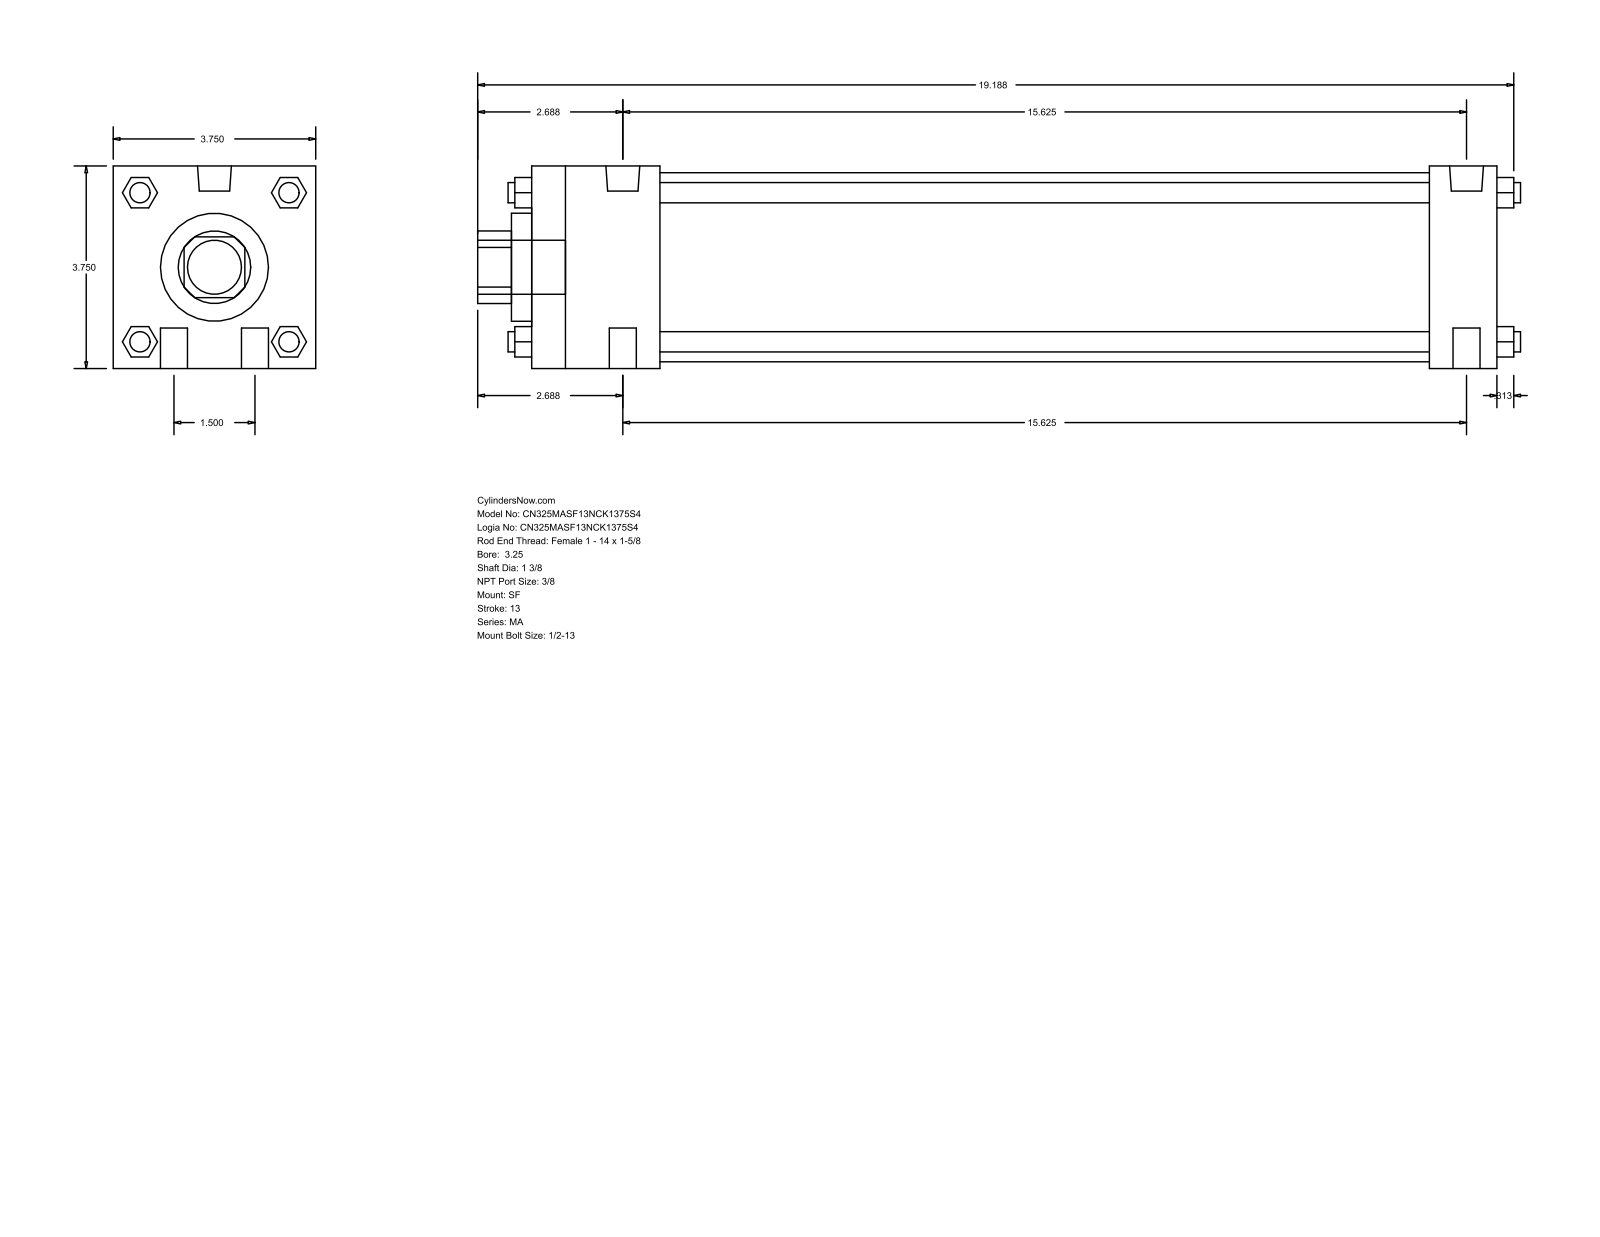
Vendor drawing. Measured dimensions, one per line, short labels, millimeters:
name: MA_SF__0325_1.375
written by: GSSL Pune (CONFIG_CONTROL_DESIGN)
unit: mm
bodies: 0 solids, 124 faces (94 planar, 30 cylindrical, 0 other)
size: 490.54 × 95.25 × 95.25
holes: 1× ⌀34.92, 1× ⌀50.8, 1× ⌀88.9
bosses: 4× ⌀12.7, 4× ⌀9.53, 2× ⌀15.93, 2× ⌀11.11, 1× ⌀25.4
rounds: 1× R17.06
face distances: 95.24, 454.03, 422.28, 31.75, 60.32, 361.96, 393.71, 9.52, 69.84, 431.8
